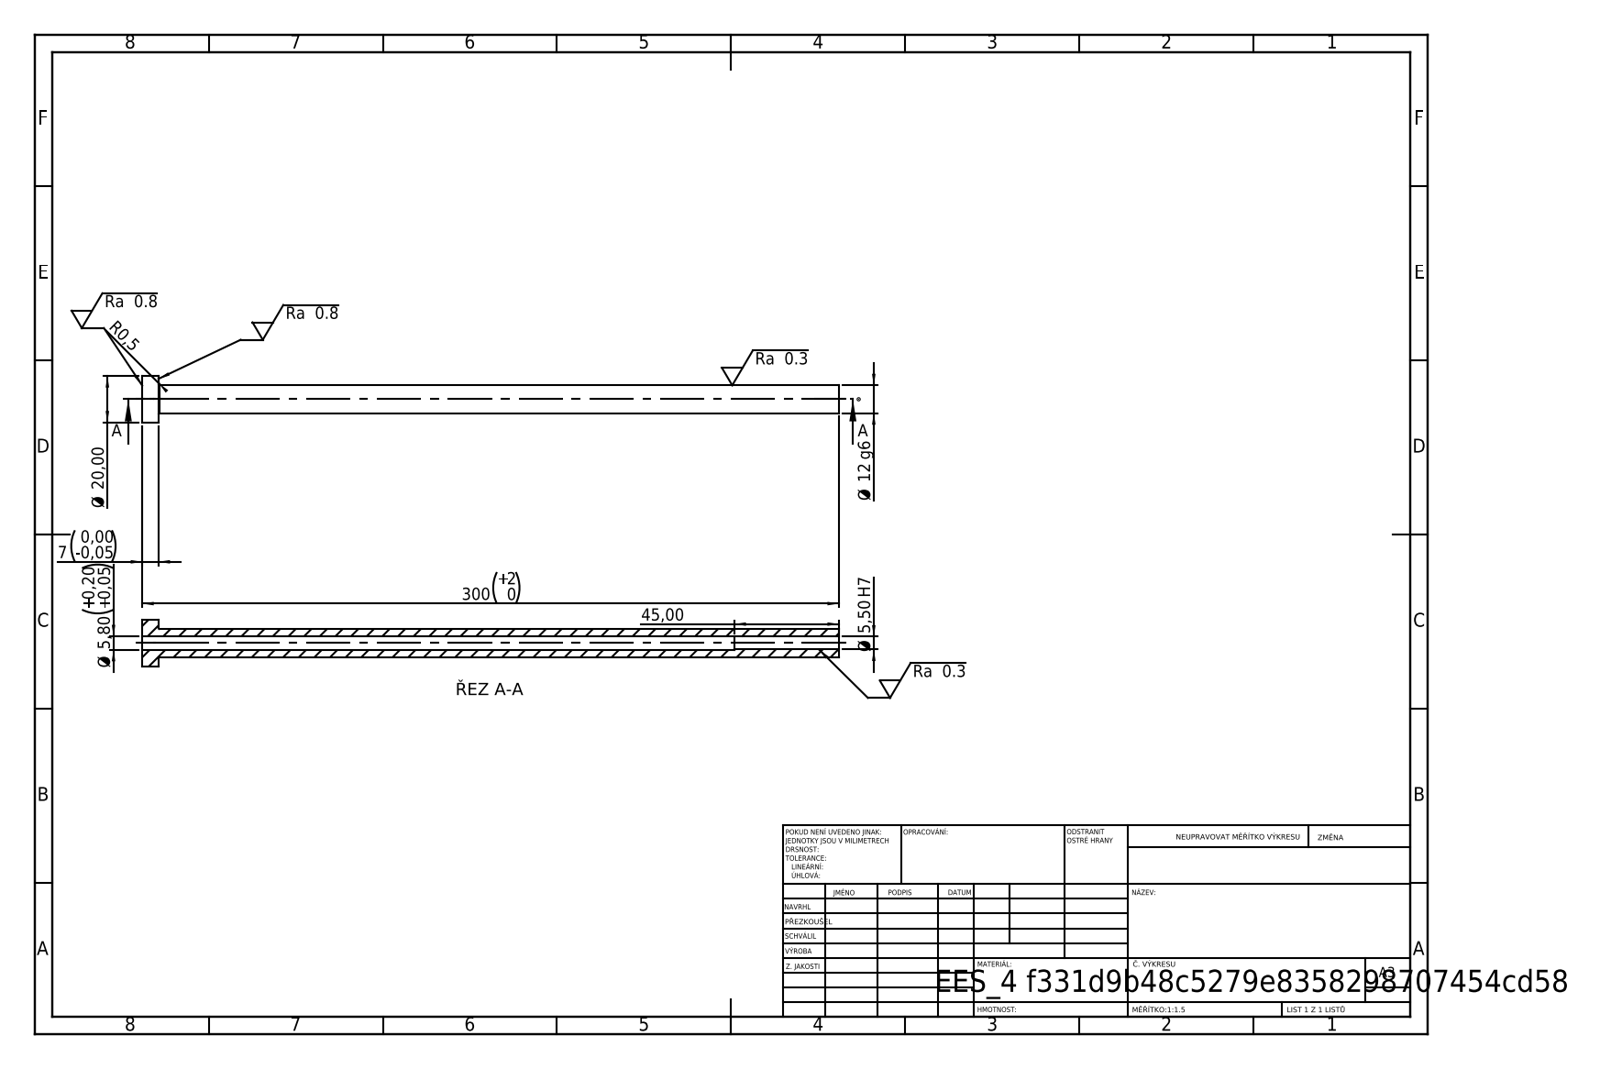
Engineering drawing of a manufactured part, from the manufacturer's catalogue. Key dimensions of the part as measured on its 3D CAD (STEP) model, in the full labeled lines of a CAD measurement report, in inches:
STEP written by: SolidWorks 2019 (CONFIG_CONTROL_DESIGN)
Units: inches
Bodies: 1 solid, 14 faces (4 planar, 8 cylindrical, 2 other)
Overall size (bounding box): 11.811 × 0.787 × 0.787
Volume: 1.68 in³ · Surface area: 27.1 in²
Round holes (diameter × count): ⌀0.217 ×1, ⌀0.228 ×1
Round bosses / shafts (diameter × count): ⌀0.787 ×1, ⌀0.472 ×1
Main face-to-face distances: 0.276, 11.811, 11.535, 10.039, 9.764, 1.772
